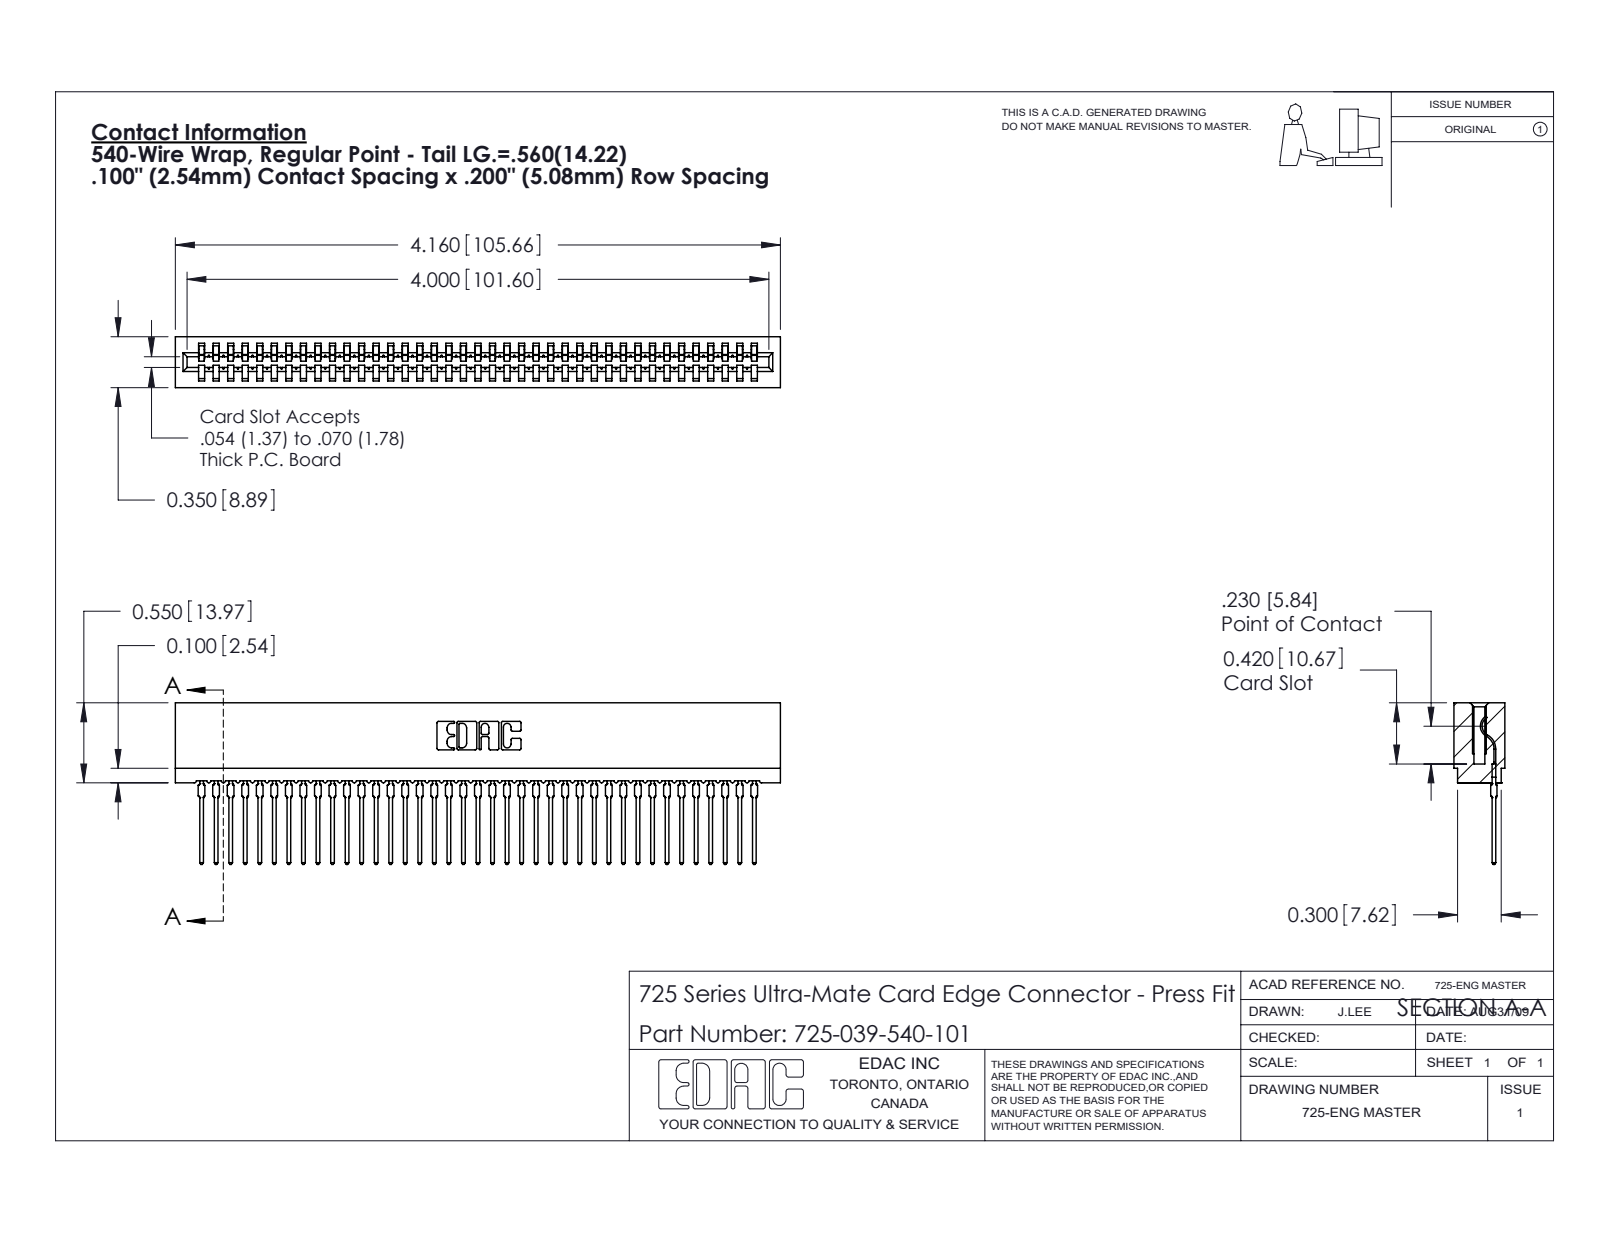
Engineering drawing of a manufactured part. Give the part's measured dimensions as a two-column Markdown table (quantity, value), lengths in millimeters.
| quantity | value |
| --- | --- |
| part name | 725 Part_Insulator Option - 01; 745-292-001_540; 725-039-540-101 |
| STEP written by | SolidWorks 2020 (CONFIG_CONTROL_DESIGN) |
| units | millimeters |
| bodies | 40 solids, 4463 faces (2668 planar, 781 cylindrical, 1014 other) |
| overall size | 105.7 × 28.2 × 8.9 |
| volume | 8 130 mm³ |
| surface area | 16 010 mm² |
| partial cylindrical surfaces (radius × count) | 0.4 × 78, 0.5 × 78, 0.3 × 22, 0.2 × 6, 0.8 × 6, 0.1 × 4, 0.3 × 4, 0.7 × 3 |
| main face-to-face distances | 8.9, 5.1, 5.4, 3.5, 1.6, 7.3, 2.5, 1.1, 7.7, 2.4 |
